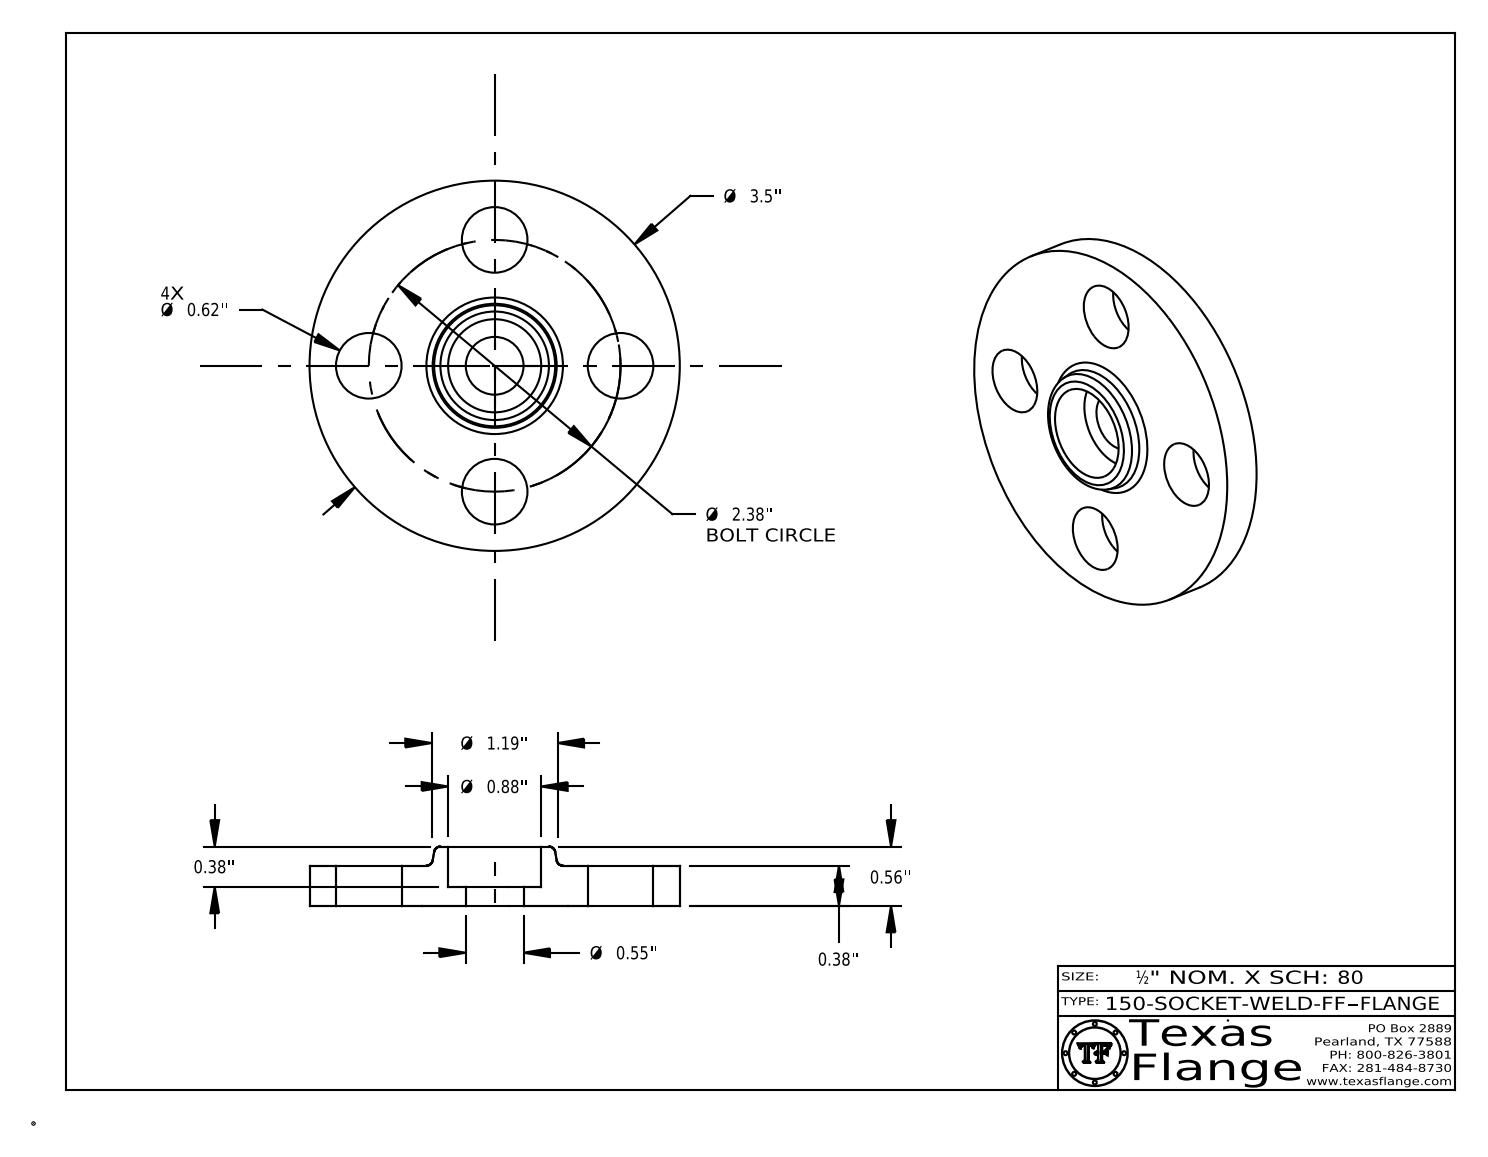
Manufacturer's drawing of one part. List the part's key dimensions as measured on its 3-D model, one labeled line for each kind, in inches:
Part name (STEP PRODUCT): 150-SOCKET-WELD-FF
STEP written by: CATIA V5 STEP AP214 (AUTOMOTIVE_DESIGN)
Units: inches
Bodies: 1 solid, 410 faces (370 planar, 34 cylindrical, 6 other)
Overall size (bounding box): 3.5 × 3.5 × 0.56
Volume: 3.113 in³ · Surface area: 25.38 in²
Round holes (diameter × count): ⌀0.62 ×4, ⌀0.495 ×1, ⌀0.546 ×1, ⌀0.88 ×1
Round bosses / shafts (diameter × count): ⌀0.03 ×8, ⌀3.5 ×1, ⌀0.39 ×1
Main face-to-face distances: 0.38, 0.18, 0.2, 0.56, 0.365, 0.185, 0.015, 0.195, 0.148, 0.145
Hole centre spacings: 1.19, 1.683, 0.911, 2.199, 2.38, 1.19
